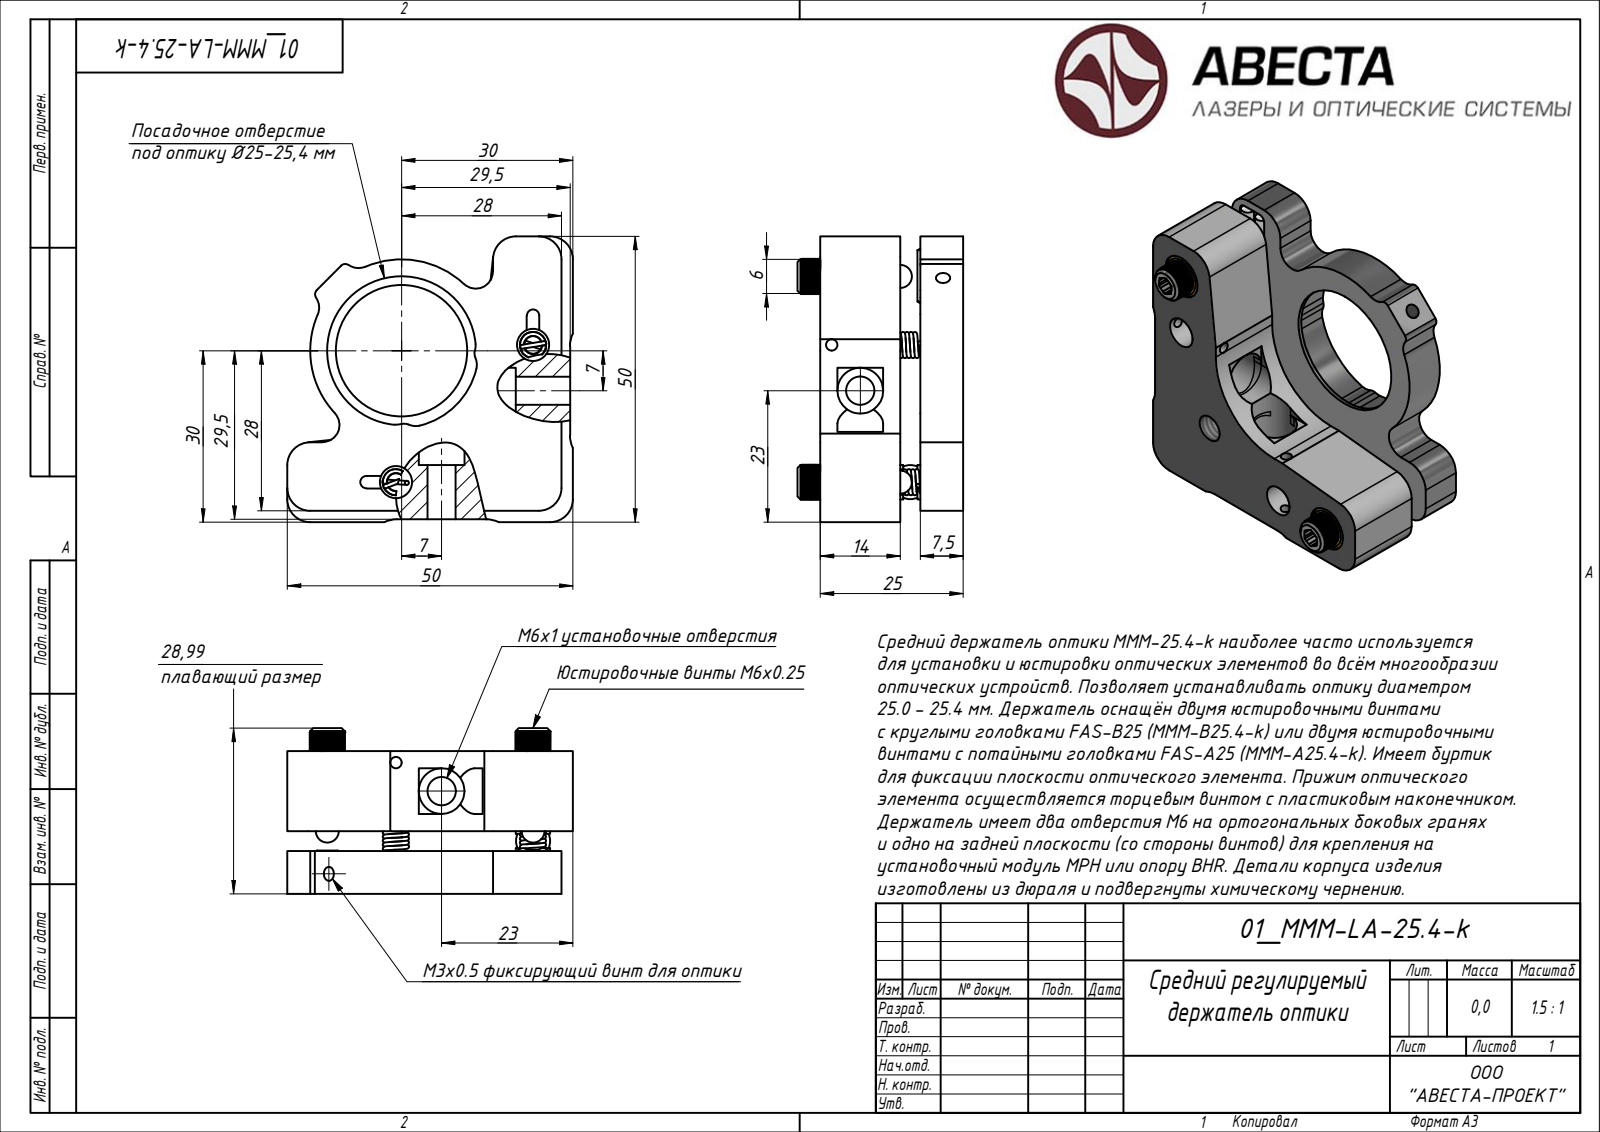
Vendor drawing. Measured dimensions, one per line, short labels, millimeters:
written by: ST-DEVELOPER v15 (AUTOMOTIVE_DESIGN)
unit: mm
bodies: 11 solids, 302 faces (114 planar, 0 cylindrical, 188 other)
size: 50 × 50 × 41.6
volume: 26 695 mm³; area: 15 700 mm²
face distances: 7.5, 14, 10.99, 17.49, 24.99, 3.49, 2, 1.5, 0.5, 48
